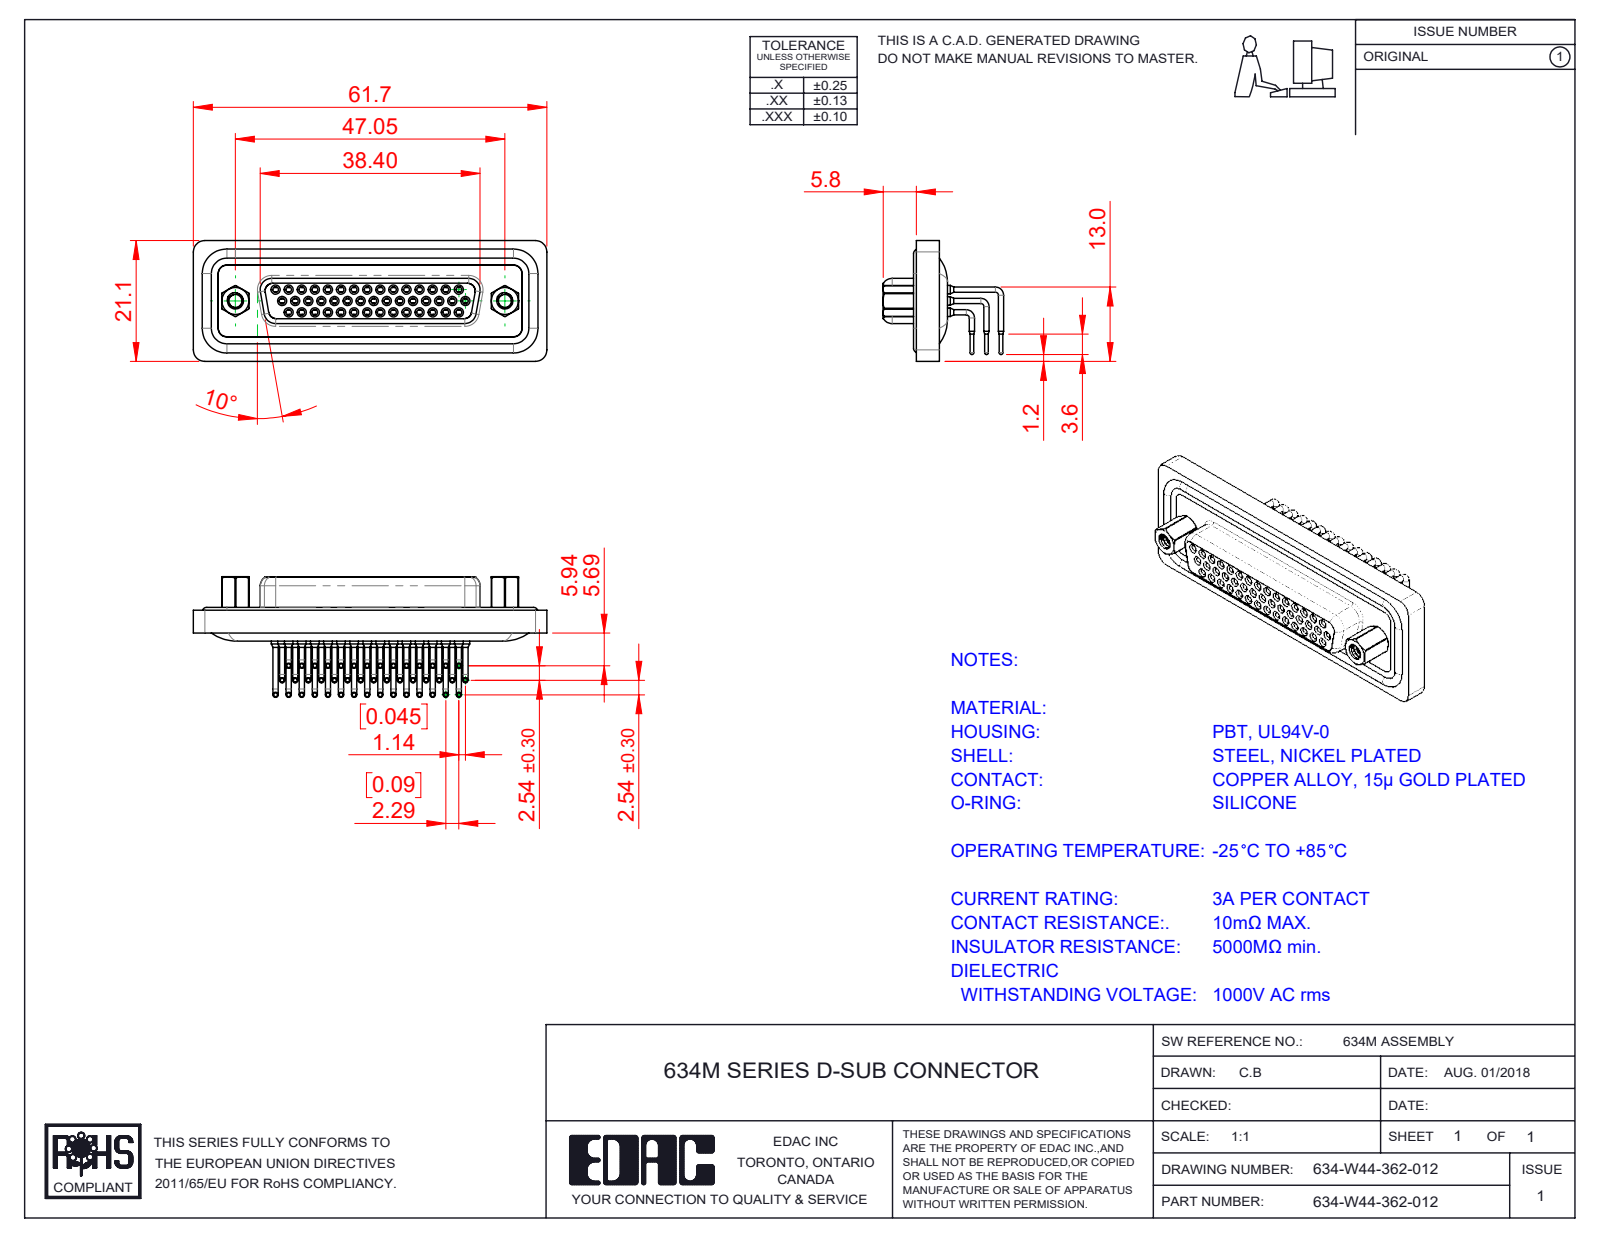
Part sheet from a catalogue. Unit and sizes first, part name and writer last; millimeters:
Units: millimetres
Overall size (bounding box): 61.74 × 21.52 × 21.1
Round holes (diameter × count): ⌀1 ×44, ⌀1.1 ×44, ⌀1.5 ×44, ⌀1.7 ×44, ⌀1.8 ×44, ⌀2 ×44, ⌀2.26 ×2, ⌀2.29 ×2, ⌀4 ×2, ⌀4.8 ×2, ⌀5 ×2
Round bosses / shafts (diameter × count): ⌀0.9 ×88, ⌀1.6 ×48, ⌀0.65 ×44, ⌀1.5 ×23, ⌀4.9 ×2, ⌀2.79 ×2, ⌀5 ×1
Partial cylindrical surfaces — rounded edges, fillets, slot ends (radius × count): R2 ×14, R1.5 ×13, R1.35 ×8, R2.7 ×6, R0.5 ×4, R0.9 ×4, R1.6 ×4, R1.75 ×4
Main face-to-face distances: 0.4, 1.8, 1.6, 2.5, 2.9, 1.1, 7.45, 13.65, 9.8, 5.65
Hole centre spacings: 2.28, 3.96, 2.29, 4.57, 8.24, 6.86, 11.43, 10.48
Volume: 7 451 mm³ · Surface area: 16 682 mm²
Bodies: 52 solids, 2843 faces (761 planar, 1320 cylindrical, 762 other)
Part name (STEP PRODUCT): 634W Contact Row 3; 634W Housing_44 Contacts; 634W Waterproof Housing_44 Contacts; 634W Shell_44 Contacts (+5 more)
STEP written by: SolidWorks 2023 (CONFIG_CONTROL_DESIGN)
